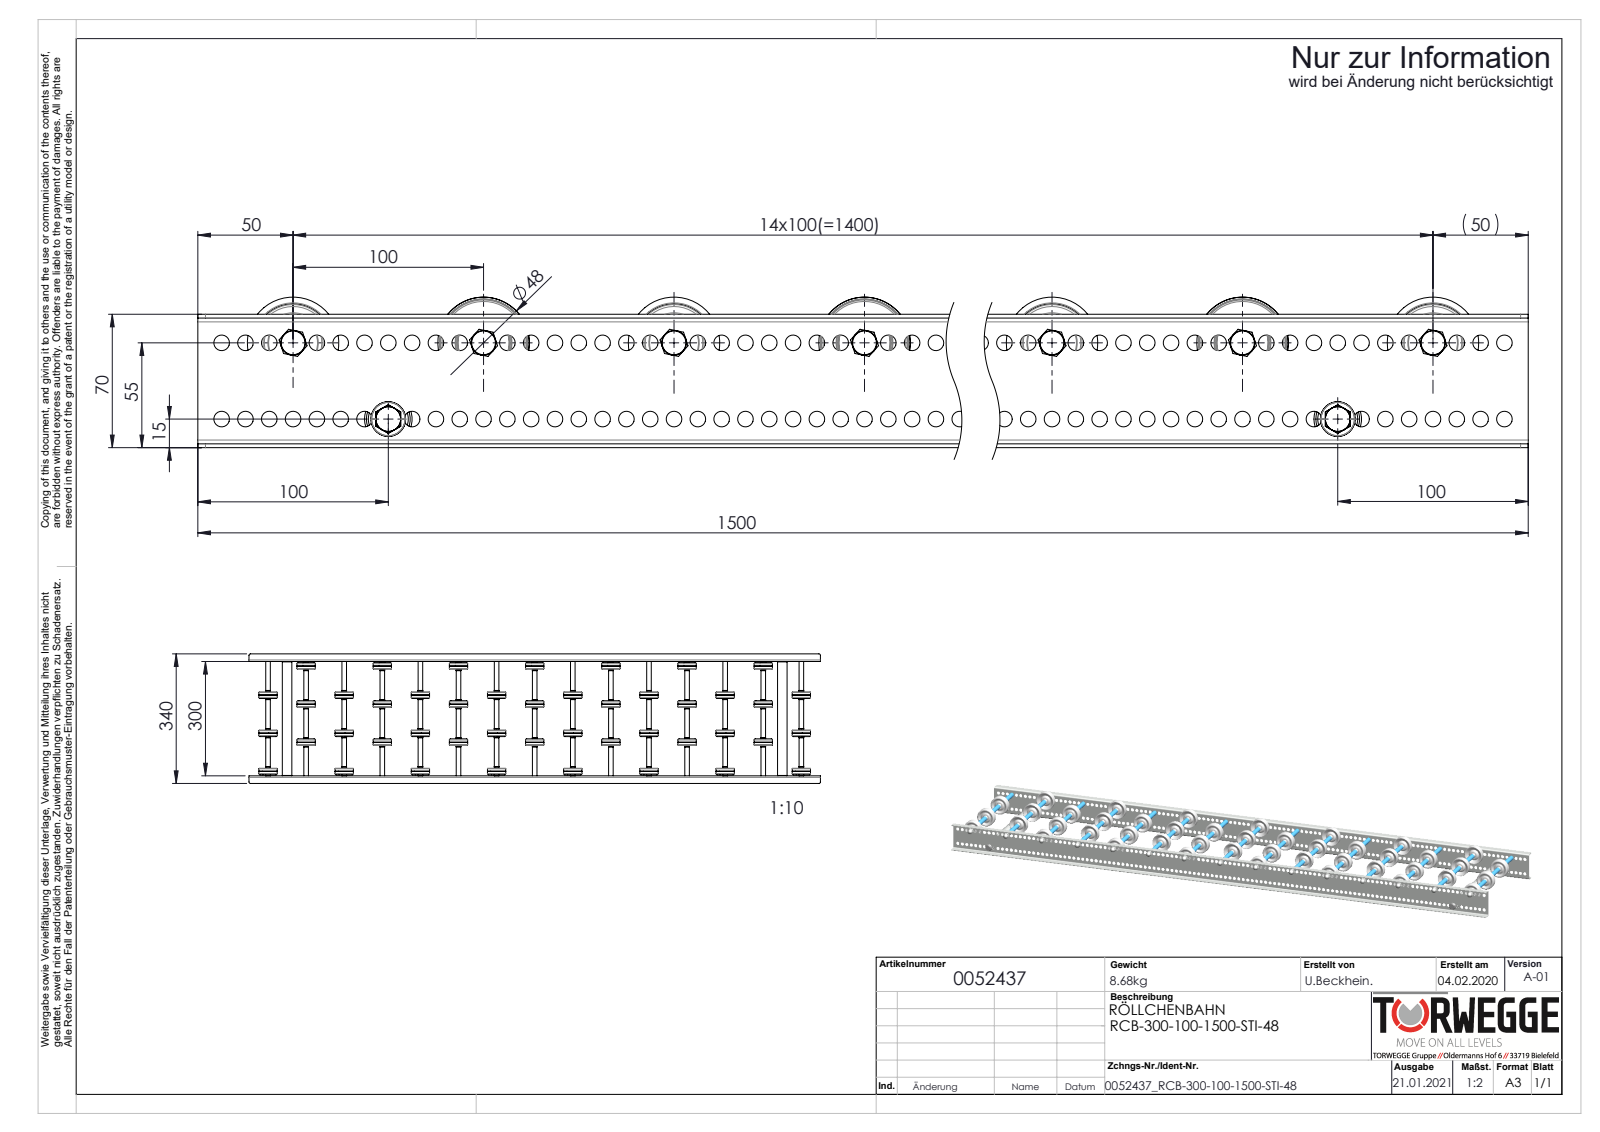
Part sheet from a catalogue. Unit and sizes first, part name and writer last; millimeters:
Units: millimetres
Overall size (bounding box): 1500 × 340 × 79
Round holes (diameter × count): ⌀8.2 ×238, ⌀6.65 ×15, ⌀8 ×15, ⌀9.65 ×15, ⌀15 ×15, ⌀41 ×15, ⌀6.8 ×2, ⌀21 ×2
Round bosses / shafts (diameter × count): ⌀48 ×15, ⌀13 ×15, ⌀12.5 ×15, ⌀12.4 ×15, ⌀12 ×15, ⌀11.5 ×15, ⌀25 ×2, ⌀8 ×2
Partial cylindrical surfaces — rounded edges, fillets, slot ends (radius × count): R4 ×8, R2 ×4
Main face-to-face distances: 2, 302, 100, 68, 304, 300, 76, 12, 88, 200
Hole centre spacings: 12.5, 25, 37.5, 50, 62.5, 75, 87.5, 100
Volume: 2 040 000 mm³ · Surface area: 1 644 000 mm²
Bodies: 192 solids, 6062 faces (1200 planar, 2508 cylindrical, 2354 other)
Part name (STEP PRODUCT): S106837_Gewindestange-M8-KFG_L320; K0011528_2200-48-8; Hutmutter_DIN_1587_M8; Profil_LRB-20x70x20x2_KFG_S100201_U-PROFIL-20-70-20-2-LRB-L=1500 (+5 more)
STEP written by: SolidWorks 2020 (AUTOMOTIVE_DESIGN)
